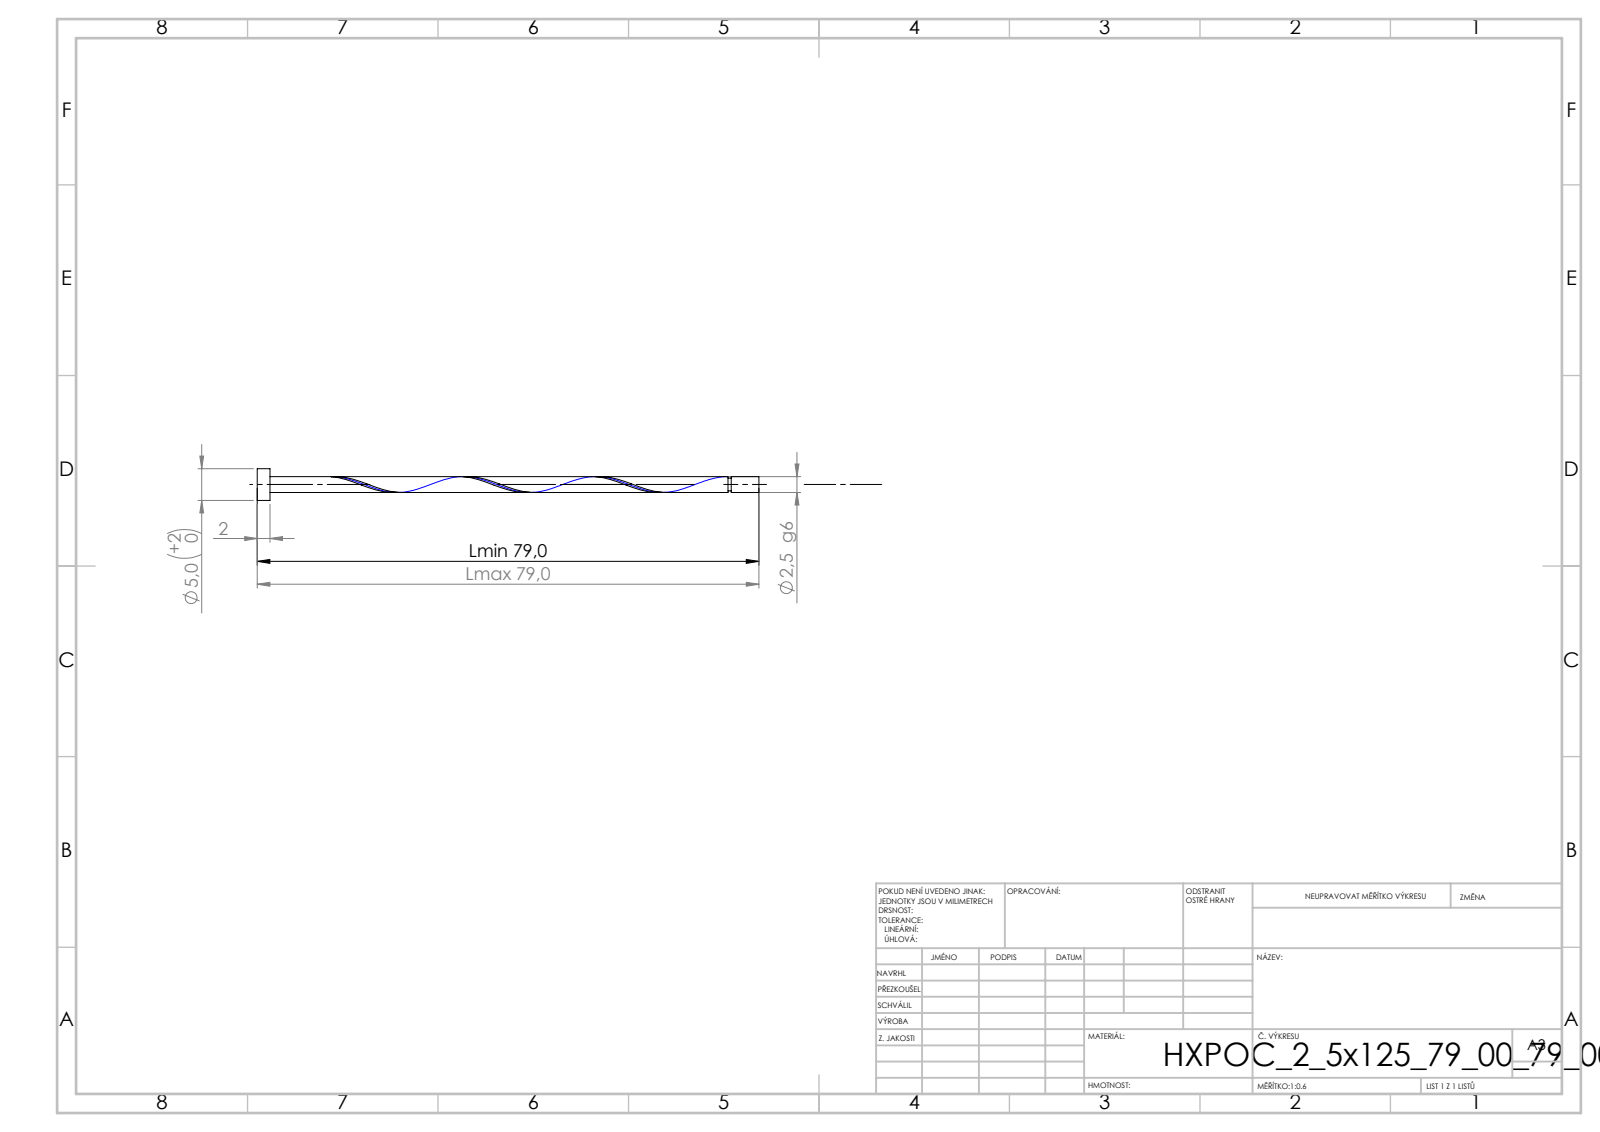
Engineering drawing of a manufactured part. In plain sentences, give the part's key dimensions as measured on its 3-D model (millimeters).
Its 3-D file was written by "SolidWorks 2019 (CONFIG_CONTROL_DESIGN)". It is 1 solid with 21 faces: 6 planar, 14 cylindrical and 1 other. Overall it measures 79 by 5 by 5 millimeters. Its volume is 410 cubic millimeters and its surface area 694 square millimeters. Round bosses or shafts: 1 of diameter 5, 1 of diameter 2.5, 1 of diameter 2. The main face-to-face distances are 2, 79, 77, 74.65, 72.65, 4.35, 74.15, 72.15, 0.5, 4.85.
